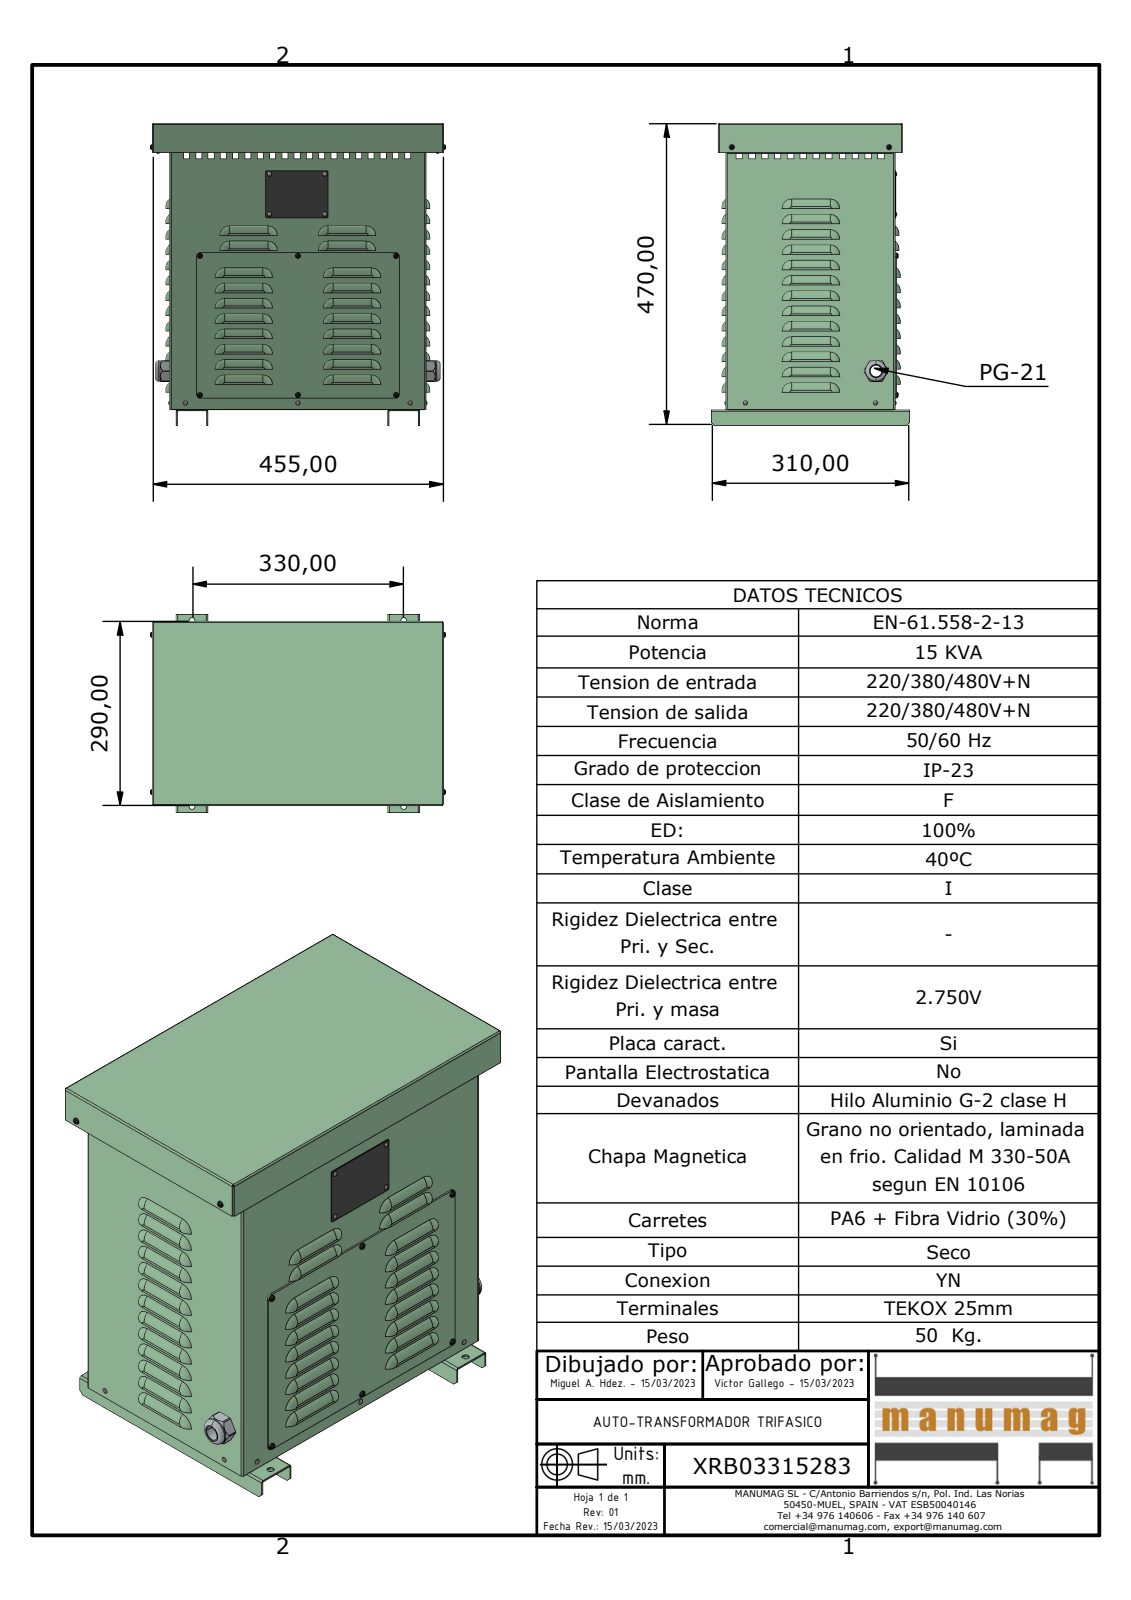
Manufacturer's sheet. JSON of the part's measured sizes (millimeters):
{"part_name": "XRB03315283; JE015 - JE020 - JE025 EXPORT CUERPO; JE015 - JE020 - JE025 EXPORT BASE; JE015 - JE020 - JE025 EXPORT PATA (+6 more)", "step_written_by": "Autodesk Inventor 2023 (AUTOMOTIVE_DESIGN)", "units": "millimeters", "bodies": {"solids": 33, "faces": 2242, "planar": 1225, "cylindrical": 489, "other": 528}, "overall_size": [474.44, 463.69, 310], "volume_mm3": 2342000, "surface_area_mm2": 2098000, "round_holes": [[3.4, 17], [4, 9], [2.3, 8], [9, 6], [5.1, 3], [8.92, 2], [18, 1], [29.9, 1]], "round_bosses_or_shafts": [[3.2, 9], [4, 8], [3.62, 8], [32.4, 1], [28.5, 1], [28.3, 1]], "partial_cylinders_radius": [[14, 118], [4, 63], [15, 49], [2, 10], [2, 9], [3.47, 8], [0.5, 6], [2.5, 6]], "face_to_face_distances": [2, 262.92, 264.92, 400.8, 447.27, 449.27, 260.92, 398.8, 402.8, 4], "hole_center_spacings": [218.1, 153.8, 154.1, 266.87, 267.05, 307.9, 332.28, 377.32]}
